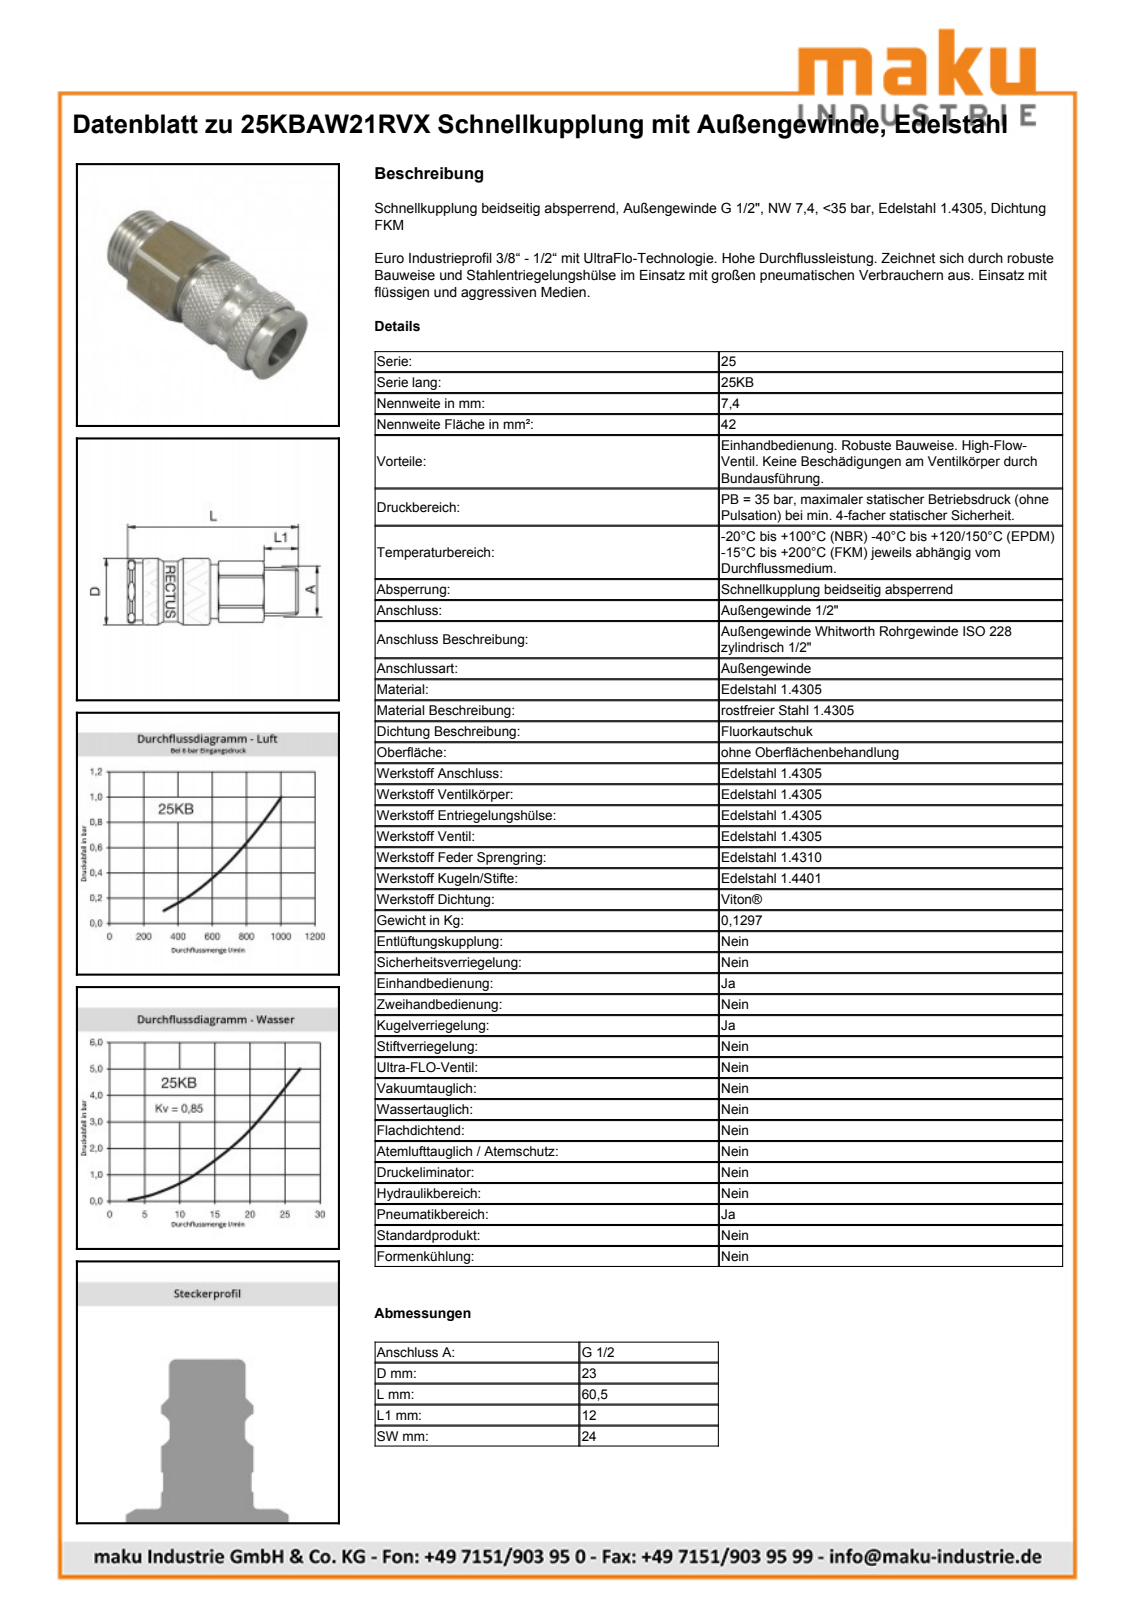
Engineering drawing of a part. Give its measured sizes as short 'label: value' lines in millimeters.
name: D105016
written by: Autodesk Inventor 2013 (AUTOMOTIVE_DESIGN)
unit: mm
bodies: 2 solids, 608 faces (210 planar, 79 cylindrical, 319 other)
size: 60.5 × 26.86 × 25.7
volume: 22 886 mm³; area: 8 615 mm²
holes: 1× ⌀17.25, 1× ⌀19.35, 1× ⌀20.05
bosses: 1× ⌀23.15, 1× ⌀21, 1× ⌀20.95, 1× ⌀20, 1× ⌀18.95, 1× ⌀16
rounds: 1× R6.61, 1× R10.4, 1× R11, 1× R13.53
face distances: 24, 60.5, 23.98, 31.45, 29.05, 48.5, 17.05, 12, 24.5, 6.95
